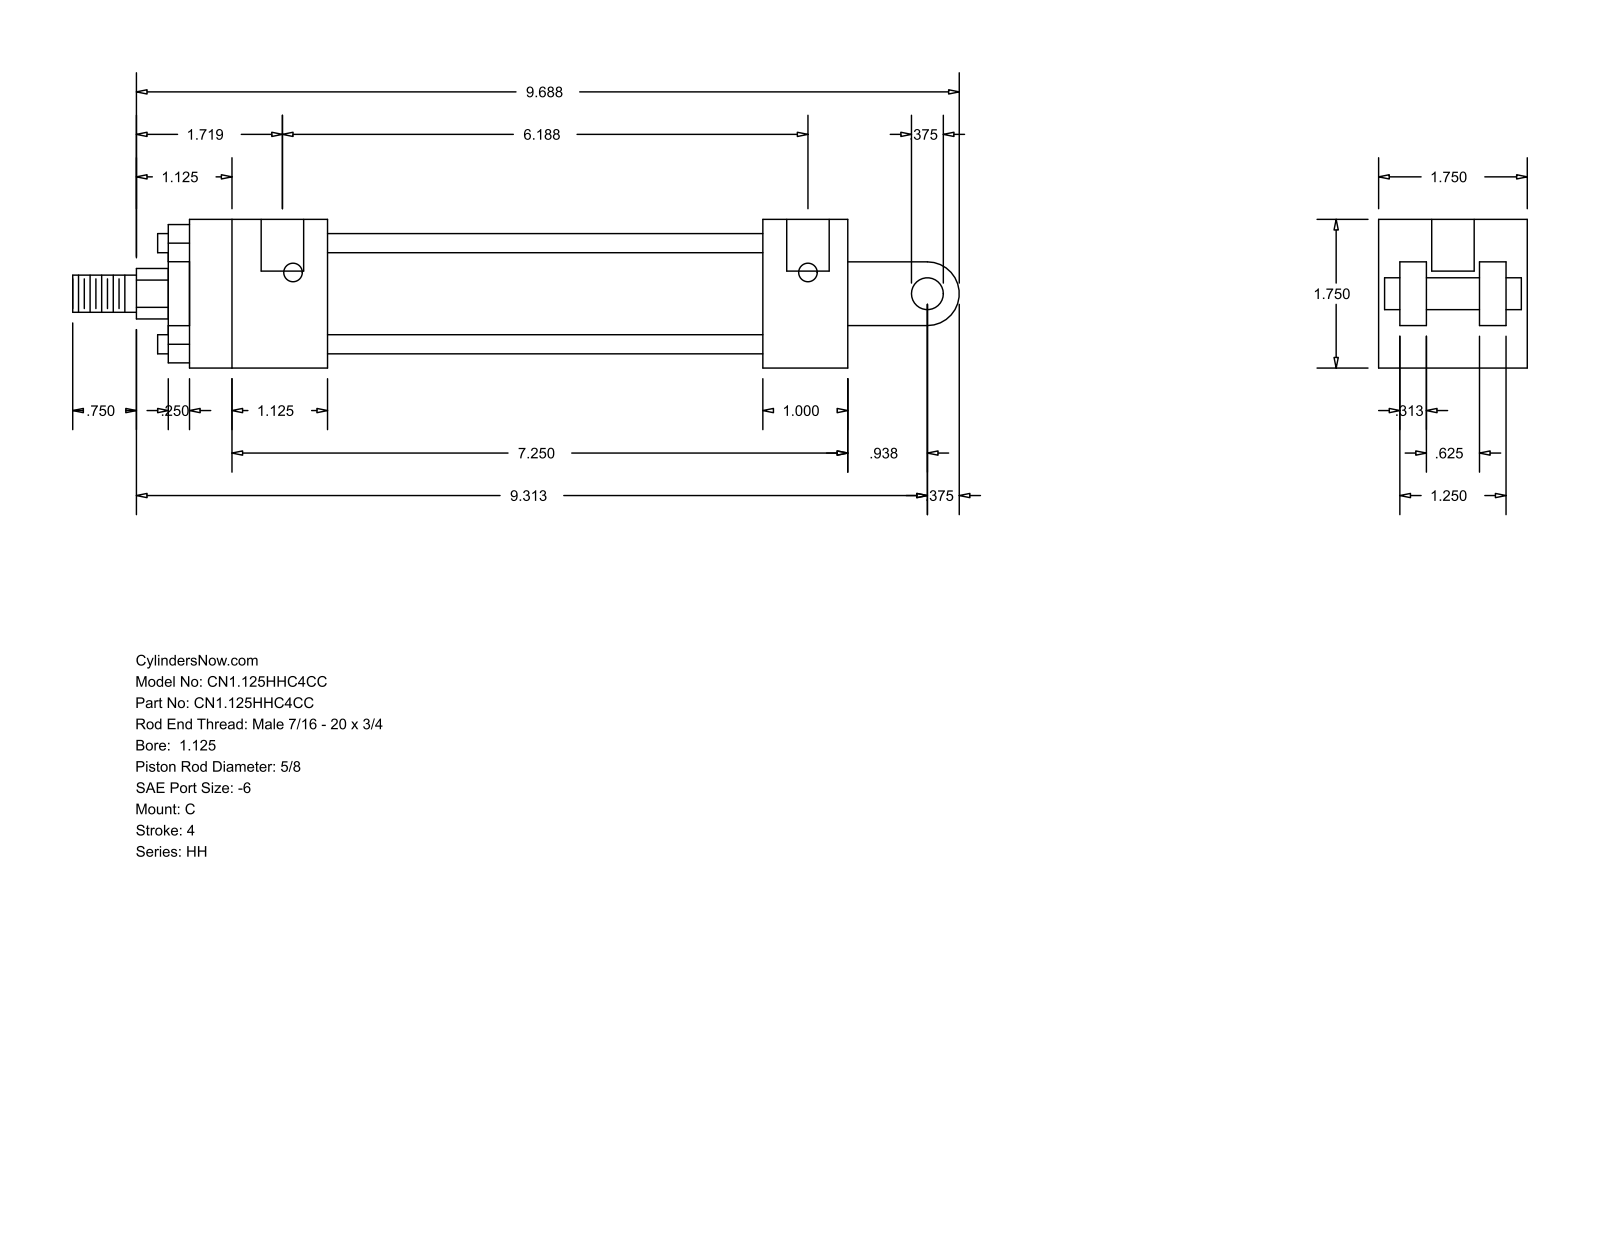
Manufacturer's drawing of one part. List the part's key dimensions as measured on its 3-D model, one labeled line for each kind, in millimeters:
Part name (STEP PRODUCT): HH_C__0112_0.625
STEP written by: GSSL Pune (CONFIG_CONTROL_DESIGN)
Units: millimetres
Bodies: 0 solids, 99 faces (70 planar, 29 cylindrical, 0 other)
Overall size (bounding box): 265.11 × 44.45 × 44.45
Round holes (diameter × count): ⌀5.56 ×4, ⌀12.7 ×2
Round bosses / shafts (diameter × count): ⌀5.71 ×4, ⌀34.92 ×1, ⌀28.57 ×1, ⌀15.88 ×1, ⌀11.11 ×1, ⌀9.53 ×1
Partial cylindrical surfaces — rounded edges, fillets, slot ends (radius × count): R7.54 ×1, R9.53 ×1
Main face-to-face distances: 44.46, 6.35, 31.76, 14.29, 25.4, 30.17, 38.11, 7.94, 23.82, 12.7
Hole centre spacings: 153.99, 3.17, 157.16
